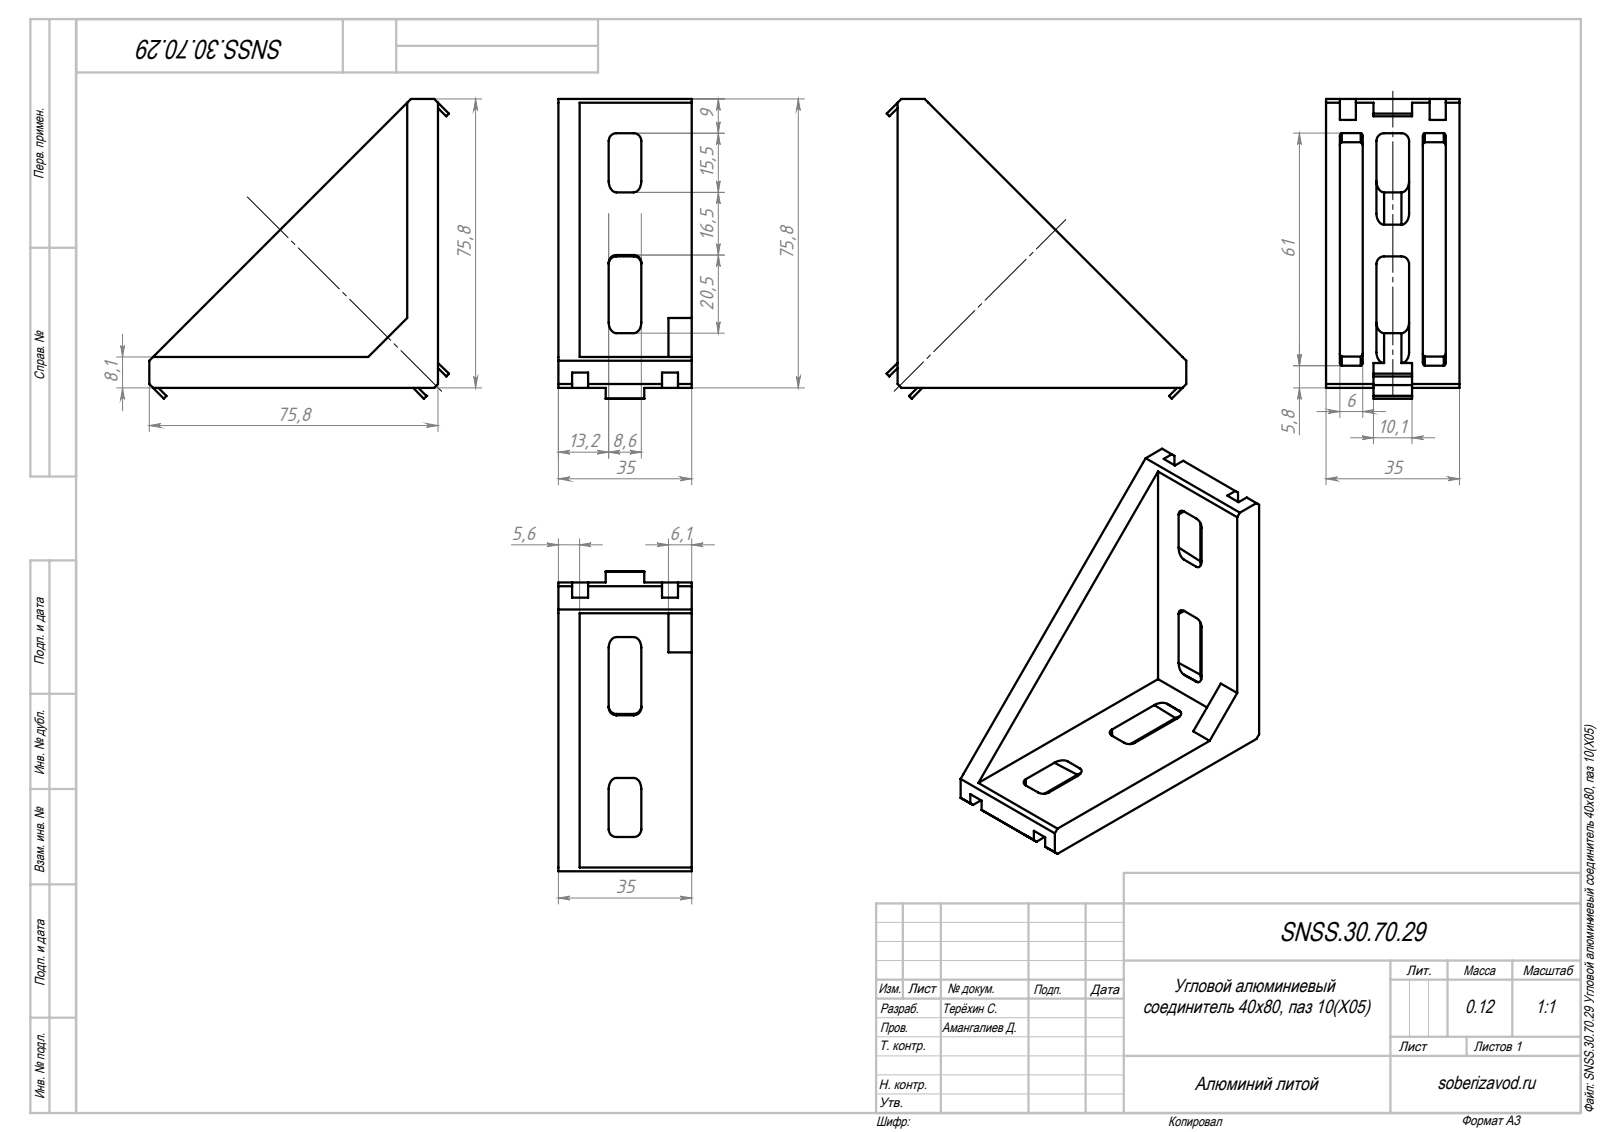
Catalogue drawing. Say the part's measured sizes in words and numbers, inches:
The part is named "SNSS.30.70.29 Угловой алюминиевый соединитель 40х80, паз 10(X05)". Its 3-D file was written by "SolidWorks 2018 (AUTOMOTIVE_DESIGN)". It is 1 solid with 135 faces: 103 planar, 32 cylindrical and 0 other. Overall it measures 3.097 by 3.097 by 1.378 inches. Its volume is 2.706 cubic inches and its surface area 29.5 square inches. Partial cylindrical surfaces (rounded edges, fillets, slot ends): 16 of radius 0.02, 16 of radius 0.079. The main face-to-face distances are 0.319, 0.22, 0.079, 0.24, 1.157, 1.378, 0.521, 0.637, 0.857, 0.857.
